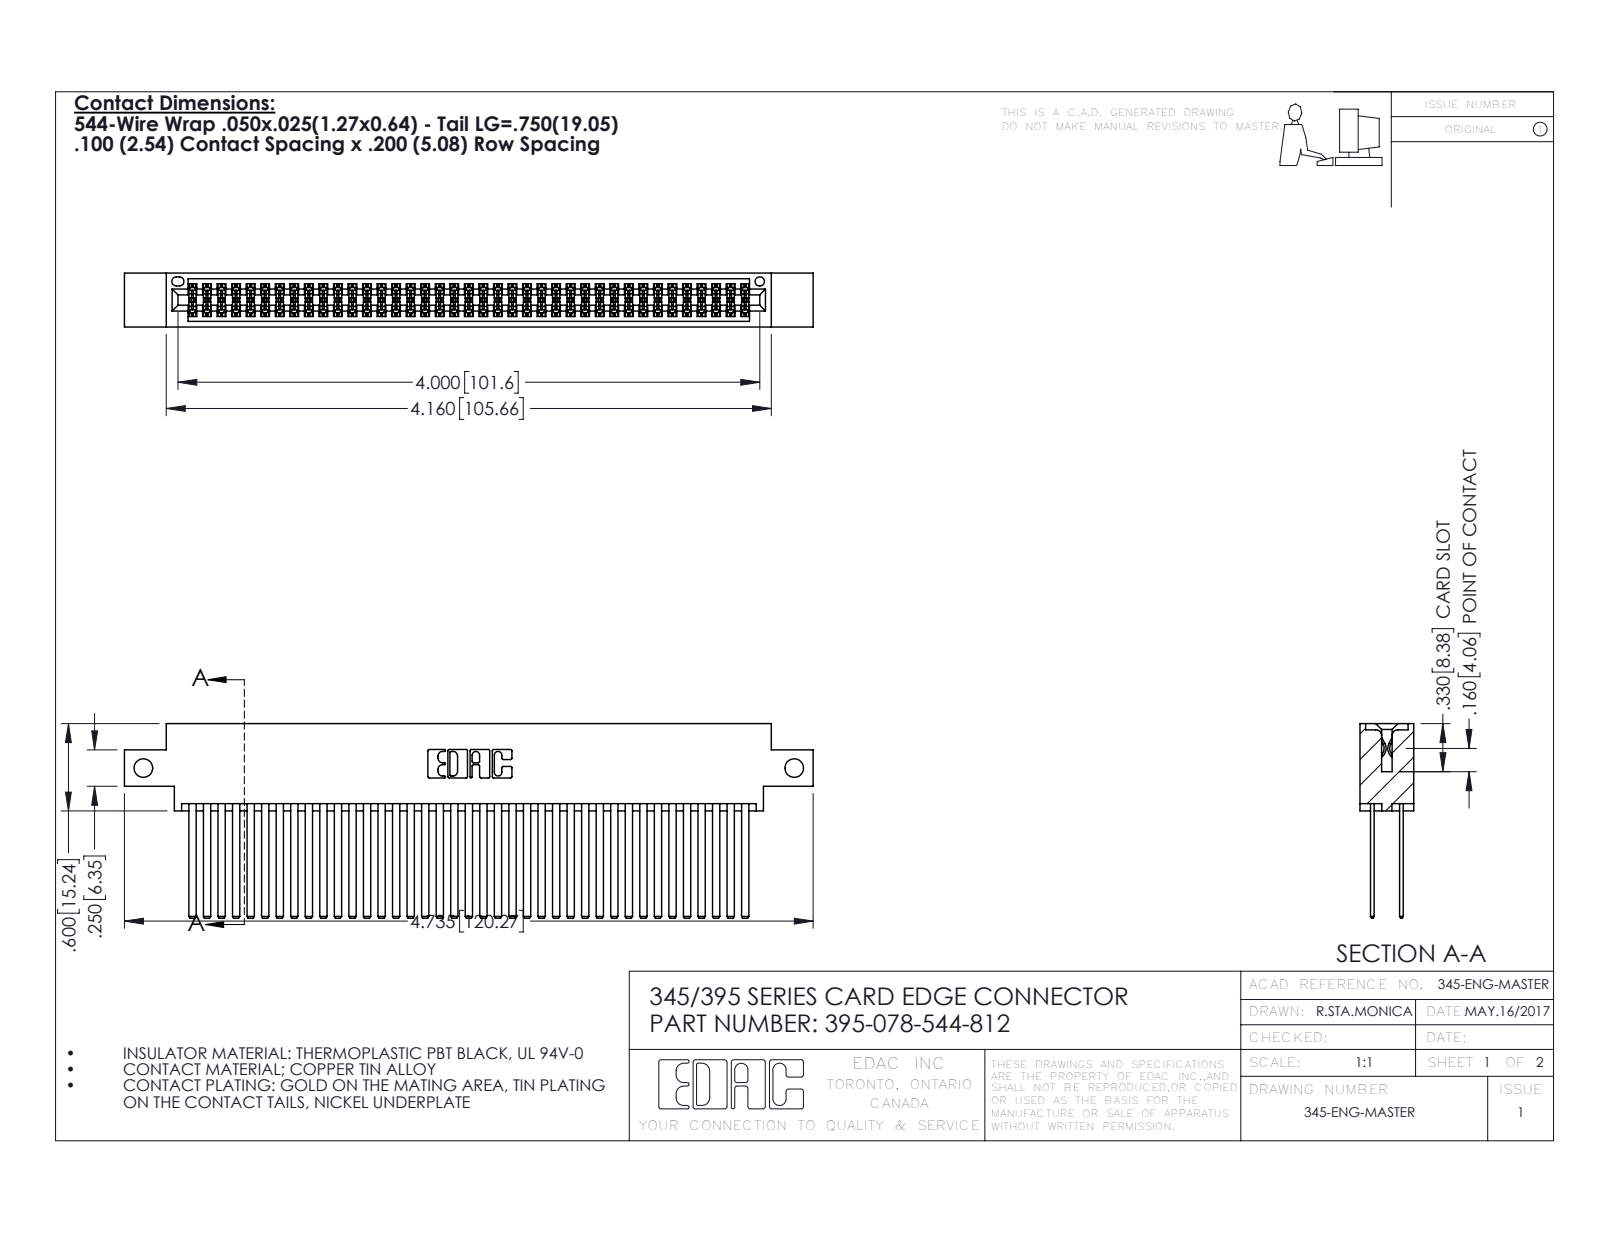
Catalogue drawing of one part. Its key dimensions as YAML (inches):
part_name: "345-292-001_345-293-144; 345 Part_0.170 Offset - Side Mount; 395-078-544-812"
step_written_by: "SolidWorks 2016 (CONFIG_CONTROL_DESIGN)"
units: inches
bodies: {solids: 79, faces: 3562, planar: 2346, cylindrical: 1216, other: 0}
overall_size: [4.735, 1.337, 0.37]
volume: 0.766
surface_area: 33.64
round_holes:
  - {diameter: 0.128, count: 2}
  - {diameter: 0.064, count: 1}
partial_cylinders:
  - {radius: 0.006, count: 117}
  - {radius: 0.01, count: 22}
  - {radius: 0.007, count: 6}
  - {radius: 0.031, count: 6}
  - {radius: 0.026, count: 3}
  - {radius: 0.014, count: 2}
  - {radius: 0.019, count: 2}
  - {radius: 0.022, count: 2}
face_to_face_distances: [0.2, 0.025, 0.298, 0.072, 0.098, 0.272, 0.225, 0.175, 0.37, 0.15]
hole_center_spacings: [4.475]
